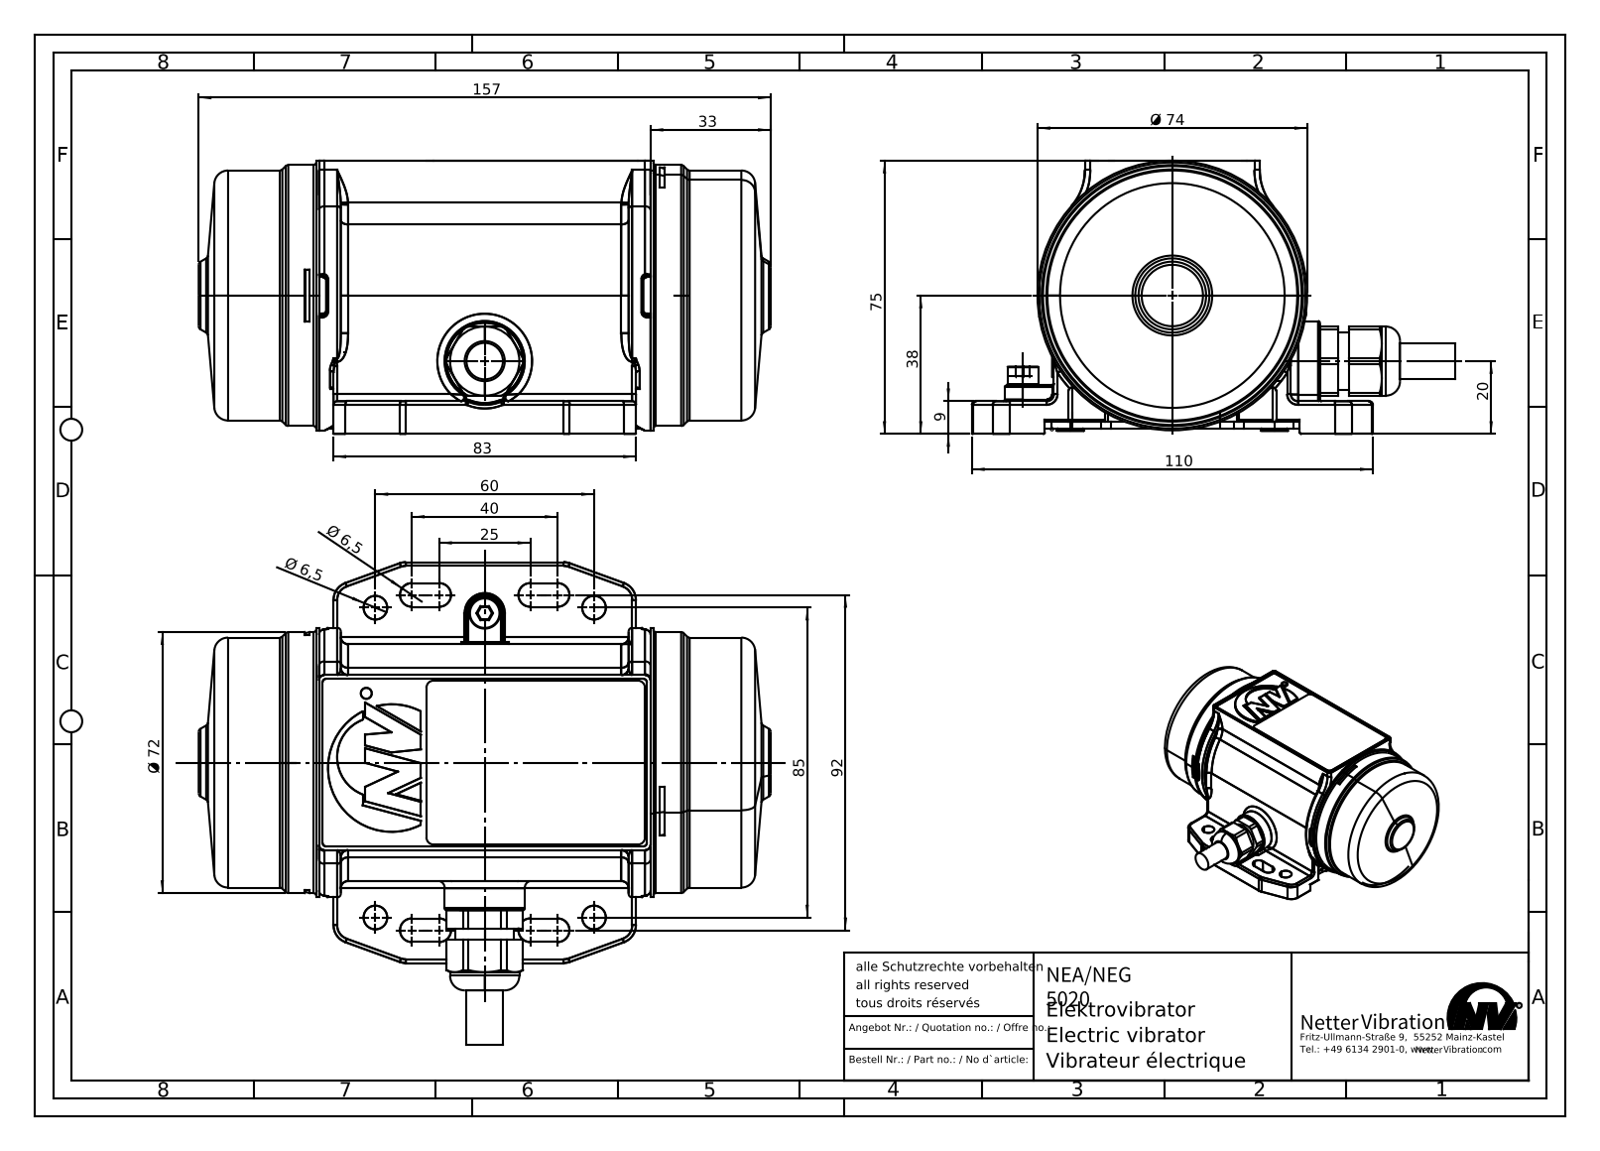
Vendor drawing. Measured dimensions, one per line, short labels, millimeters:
name: NEA-NEG 5020
written by: SolidWorks 2010 (AUTOMOTIVE_DESIGN)
unit: mm
bodies: 3 solids, 743 faces (283 planar, 241 cylindrical, 219 other)
size: 157 × 117.5 × 75
volume: 537 741 mm³; area: 94 078 mm²
holes: 4× ⌀6.5, 1× ⌀4.2, 1× ⌀10, 1× ⌀12, 1× ⌀14.5, 1× ⌀70
bosses: 4× ⌀7.5, 1× ⌀74, 1× ⌀71.6, 1× ⌀68.6, 1× ⌀67, 1× ⌀22, 1× ⌀19, 1× ⌀16
rounds: 32× R1, 29× R5, 16× R0.75, 10× R2, 8× R3.25, 7× R0.5, 4× R1.5, 2× R10
face distances: 73.5, 116, 1.5, 75, 9, 7.5, 66, 8.5, 56.5, 65
hole spacings: 30.04, 60, 85, 88.73, 104.04, 2
